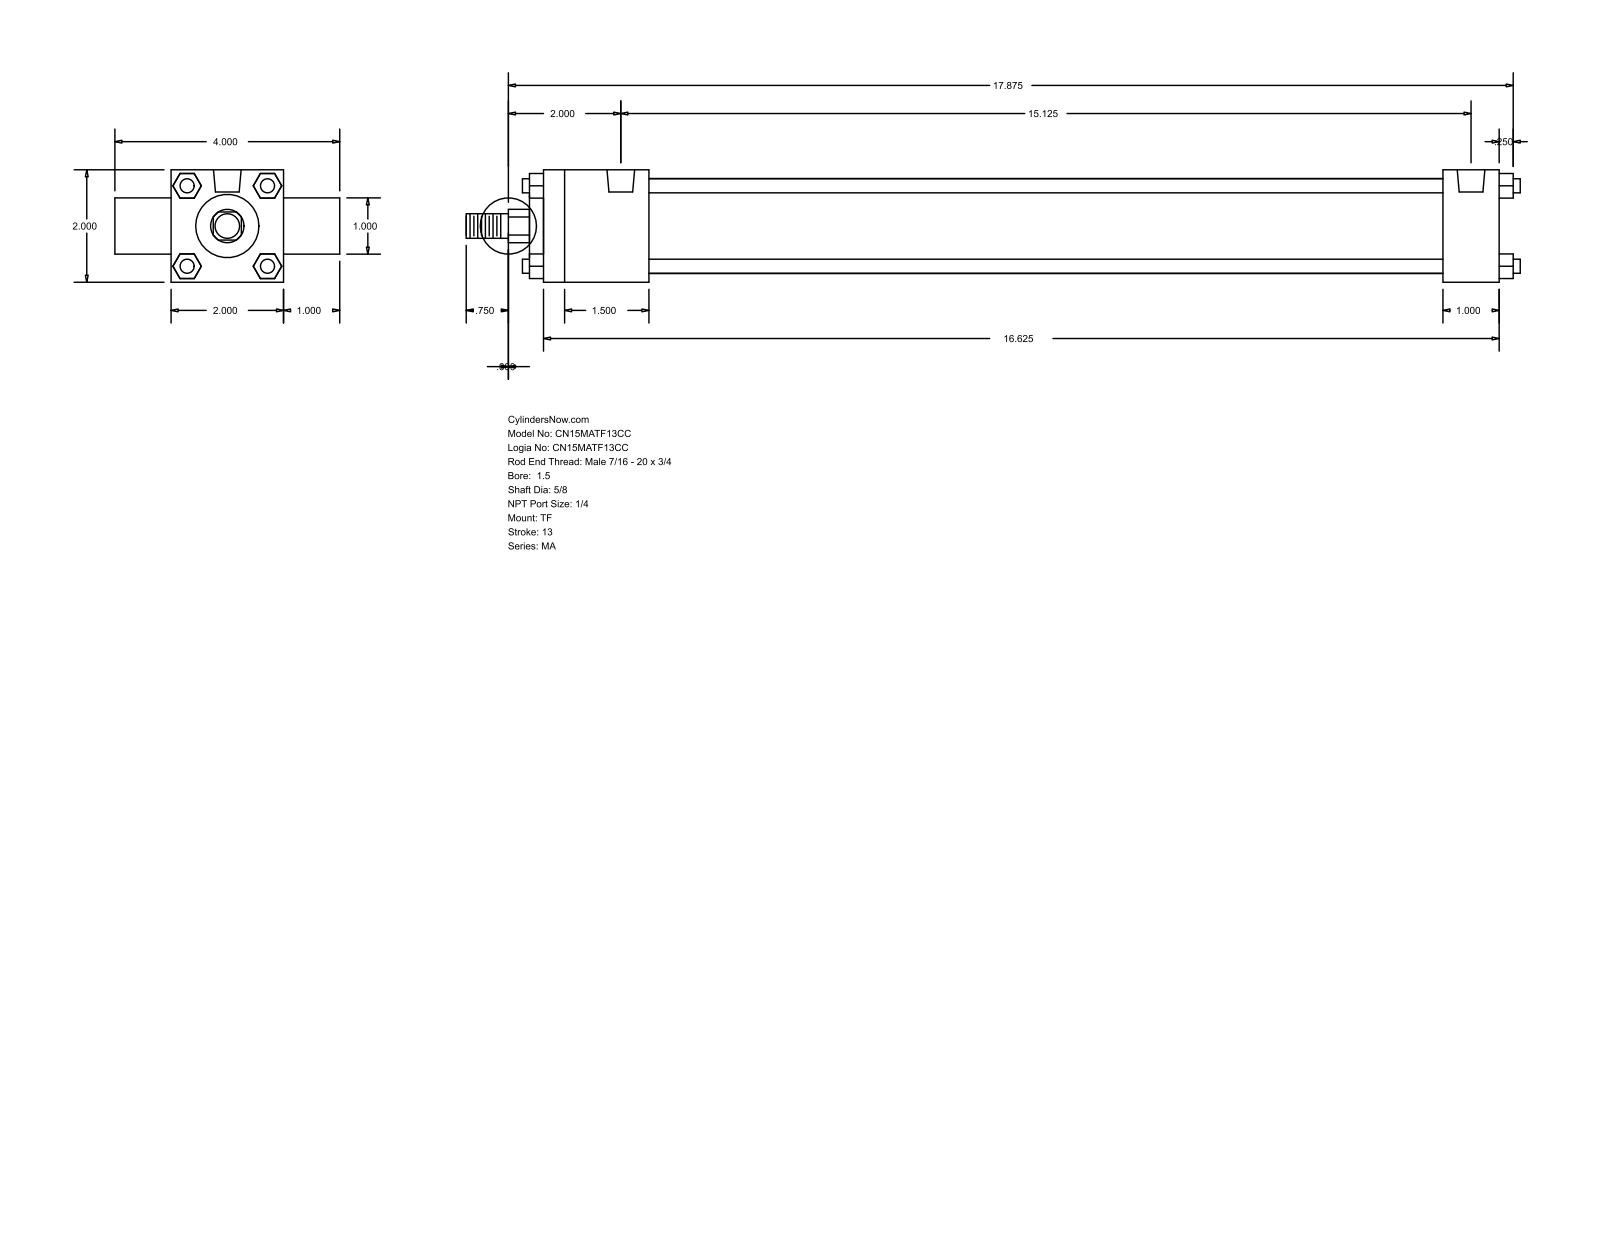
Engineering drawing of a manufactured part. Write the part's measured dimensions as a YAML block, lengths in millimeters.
part_name: "MA_TF__0150_0.625"
step_written_by: "GSSL Pune (CONFIG_CONTROL_DESIGN)"
units: millimeters
bodies: {solids: 0, faces: 120, planar: 92, cylindrical: 28, other: 0}
overall_size: [476.25, 101.6, 50.8]
round_holes:
  - {diameter: 7.94, count: 3}
  - {diameter: 12.49, count: 2}
round_bosses_or_shafts:
  - {diameter: 6.35, count: 4}
  - {diameter: 42.93, count: 1}
  - {diameter: 28.57, count: 1}
  - {diameter: 25.4, count: 1}
  - {diameter: 15.88, count: 1}
  - {diameter: 11.11, count: 1}
partial_cylinders:
  - {radius: 7.54, count: 1}
face_to_face_distances: [50.8, 431.8, 25.4, 76.2, 47.62, 406.39, 358.77, 384.18, 25.41, 6.35]
hole_center_spacings: [384.18]
